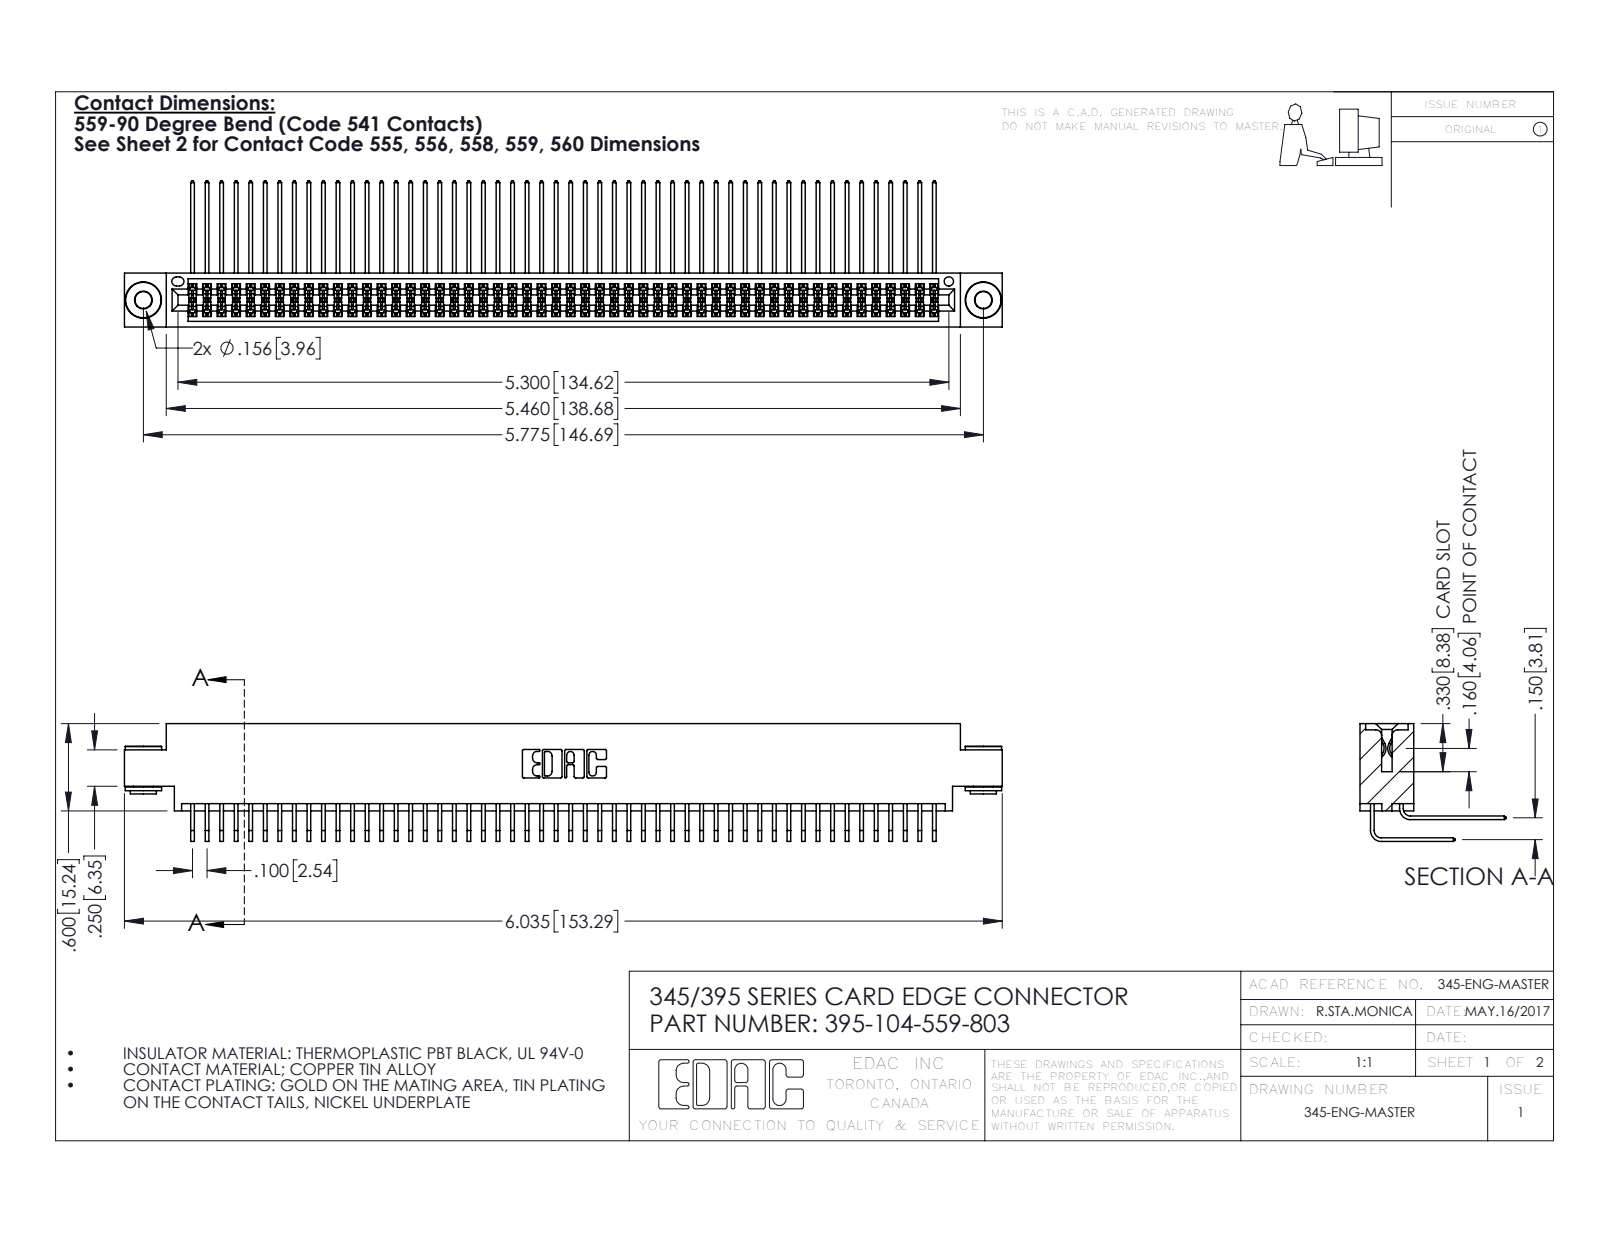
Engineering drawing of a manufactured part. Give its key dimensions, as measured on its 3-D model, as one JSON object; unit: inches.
{"part_name": "345-250-002_345-250-002-102; 395-104-559-803; 345-292-001_559 Tail - 2; 345 Part_0.170 Offset - 0.156 Dia-TH (+1 more)", "step_written_by": "SolidWorks 2016 (CONFIG_CONTROL_DESIGN)", "units": "inches", "bodies": {"solids": 107, "faces": 5576, "planar": 3734, "cylindrical": 1834, "other": 8}, "overall_size": [6.035, 1.005, 0.809], "volume_in3": 0.945, "surface_area_in2": 40.7, "round_holes": [[0.116, 2], [0.156, 2], [0.064, 1]], "round_bosses_or_shafts": [[0.25, 2], [0.18, 2], [0.136, 2]], "partial_cylinders_radius": [[0.006, 156], [0.01, 22], [0.007, 6], [0.031, 6], [0.026, 3], [0.014, 2], [0.019, 2], [0.022, 2]], "face_to_face_distances": [0.072, 0.298, 0.37, 0.2, 0.098, 0.272, 0.025, 0.175, 0.225, 0.15], "hole_center_spacings": [0.27, 5.539, 5.775]}
